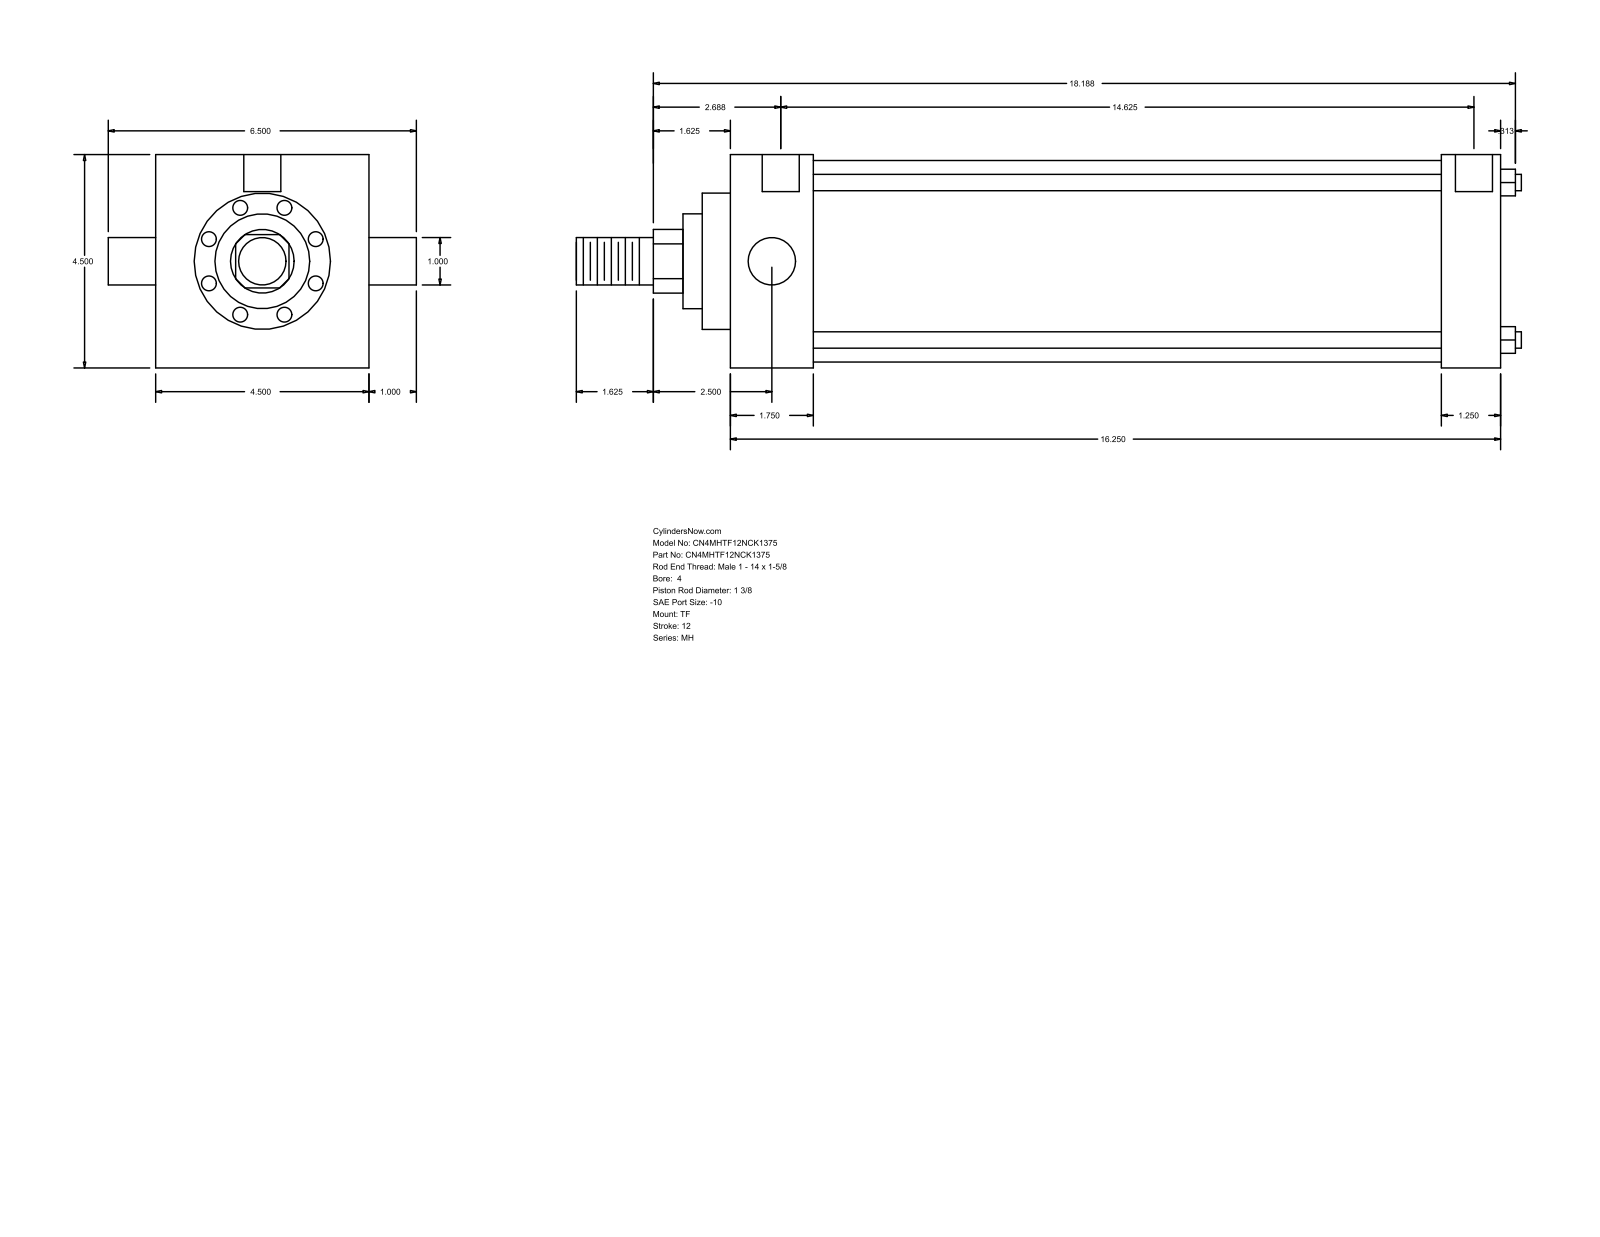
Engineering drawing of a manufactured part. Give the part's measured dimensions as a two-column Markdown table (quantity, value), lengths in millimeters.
| quantity | value |
| --- | --- |
| part name | MH_TF__0400_1.375 |
| STEP written by | GSSL Pune (CONFIG_CONTROL_DESIGN) |
| units | millimeters |
| bodies | 0 solids, 86 faces (61 planar, 25 cylindrical, 0 other) |
| overall size | 506.41 × 165.1 × 114.3 |
| round holes (diameter × count) | 8.73 × 3, 19.84 × 2 |
| round bosses / shafts (diameter × count) | 8.76 × 4, 25.4 × 2, 107.95 × 1, 73.03 × 1, 50.8 × 1, 34.92 × 1 |
| partial cylindrical surfaces (radius × count) | 17.06 × 1 |
| main face-to-face distances | 114.3, 412.75, 44.45, 368.3, 381, 336.55, 31.75, 15.08, 59.53, 396.08 |
| hole center spacings | 1.58, 1.59, 371.48, 373.06, 373.07, 374.65 |
